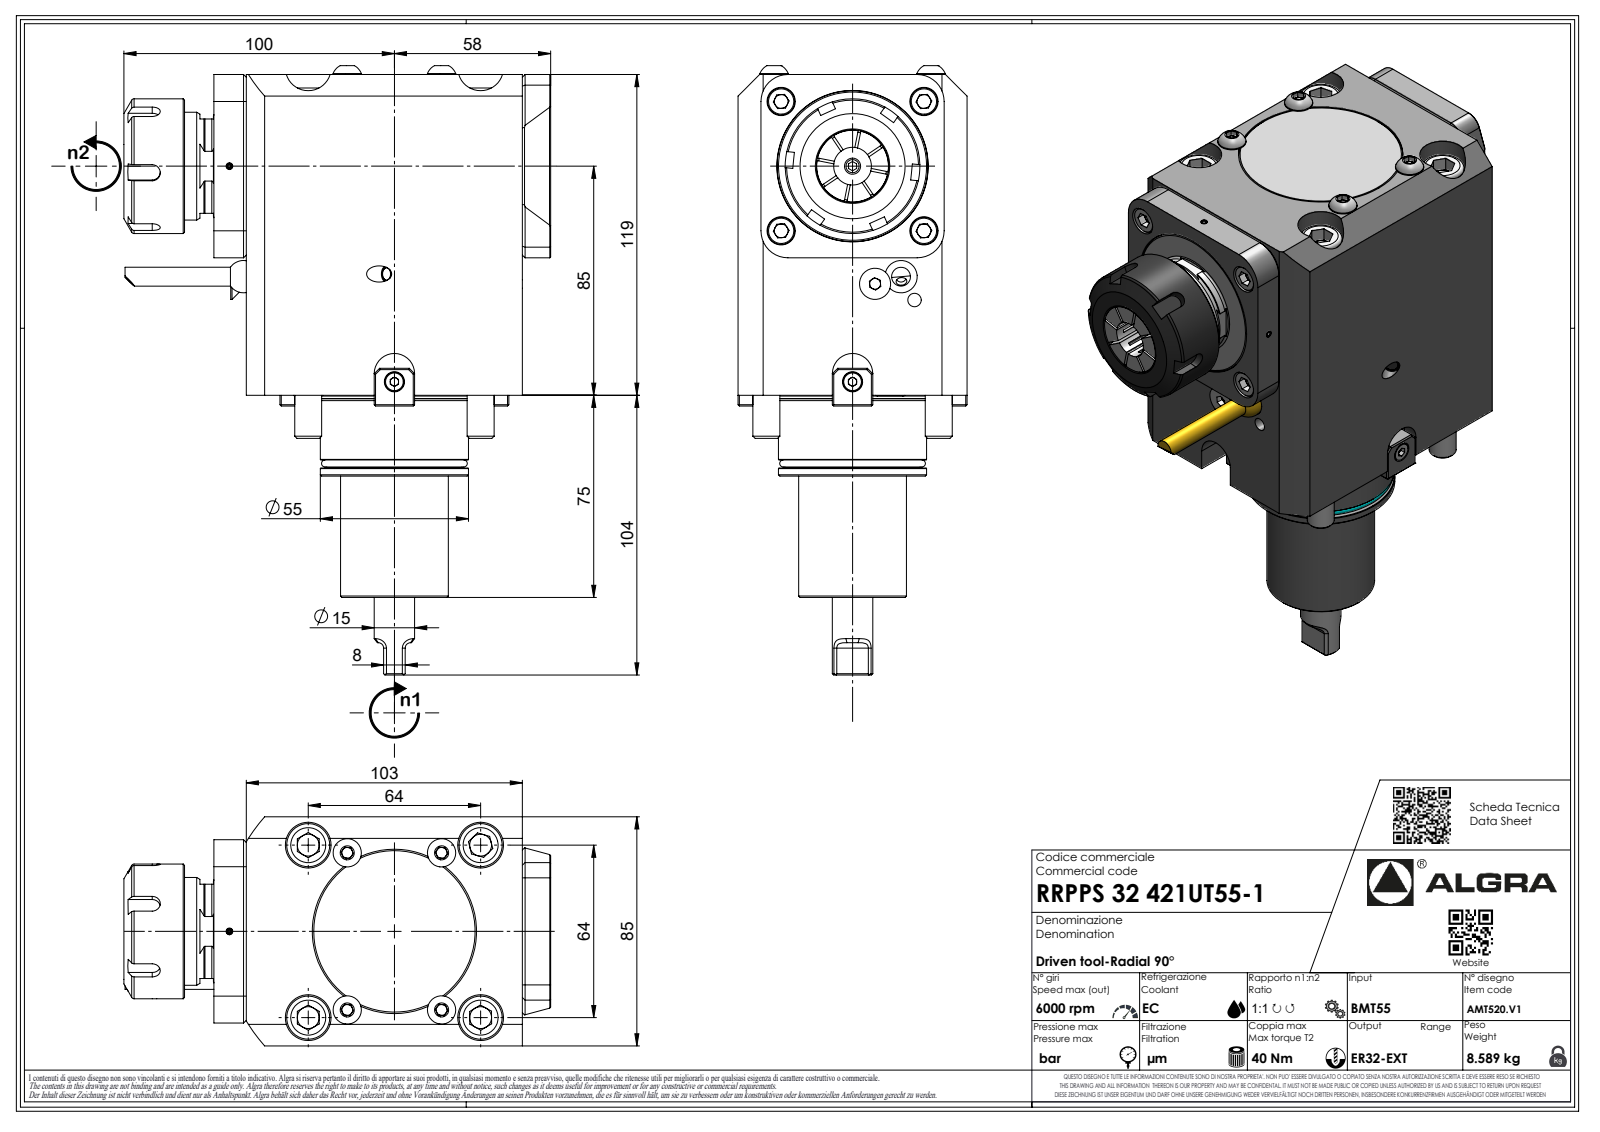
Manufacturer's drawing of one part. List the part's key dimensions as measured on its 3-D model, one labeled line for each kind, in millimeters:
Part name (STEP PRODUCT): RRPPS32421UT55-1
STEP written by: SolidWorks 2023 (AUTOMOTIVE_DESIGN)
Units: millimetres
Bodies: 1 solid, 564 faces (364 planar, 63 cylindrical, 137 other)
Overall size (bounding box): 222.8 × 158.41 × 85
Volume: 1 312 000 mm³ · Surface area: 88 355 mm²
Round holes (diameter × count): ⌀2.1 ×1, ⌀4 ×1
Round bosses / shafts (diameter × count): ⌀10 ×4, ⌀40 ×2, ⌀55 ×1, ⌀54.6 ×1, ⌀50.2 ×1, ⌀50 ×1, ⌀15 ×1, ⌀7 ×1
Partial cylindrical surfaces — rounded edges, fillets, slot ends (radius × count): R0.33 ×7, R0.52 ×7, R3.7 ×7, R3 ×6, R6 ×4, R10 ×4, R2 ×3, R0.21 ×1
Main face-to-face distances: 85, 119, 10.5, 12, 102.5, 114.5, 125, 113, 68, 51
